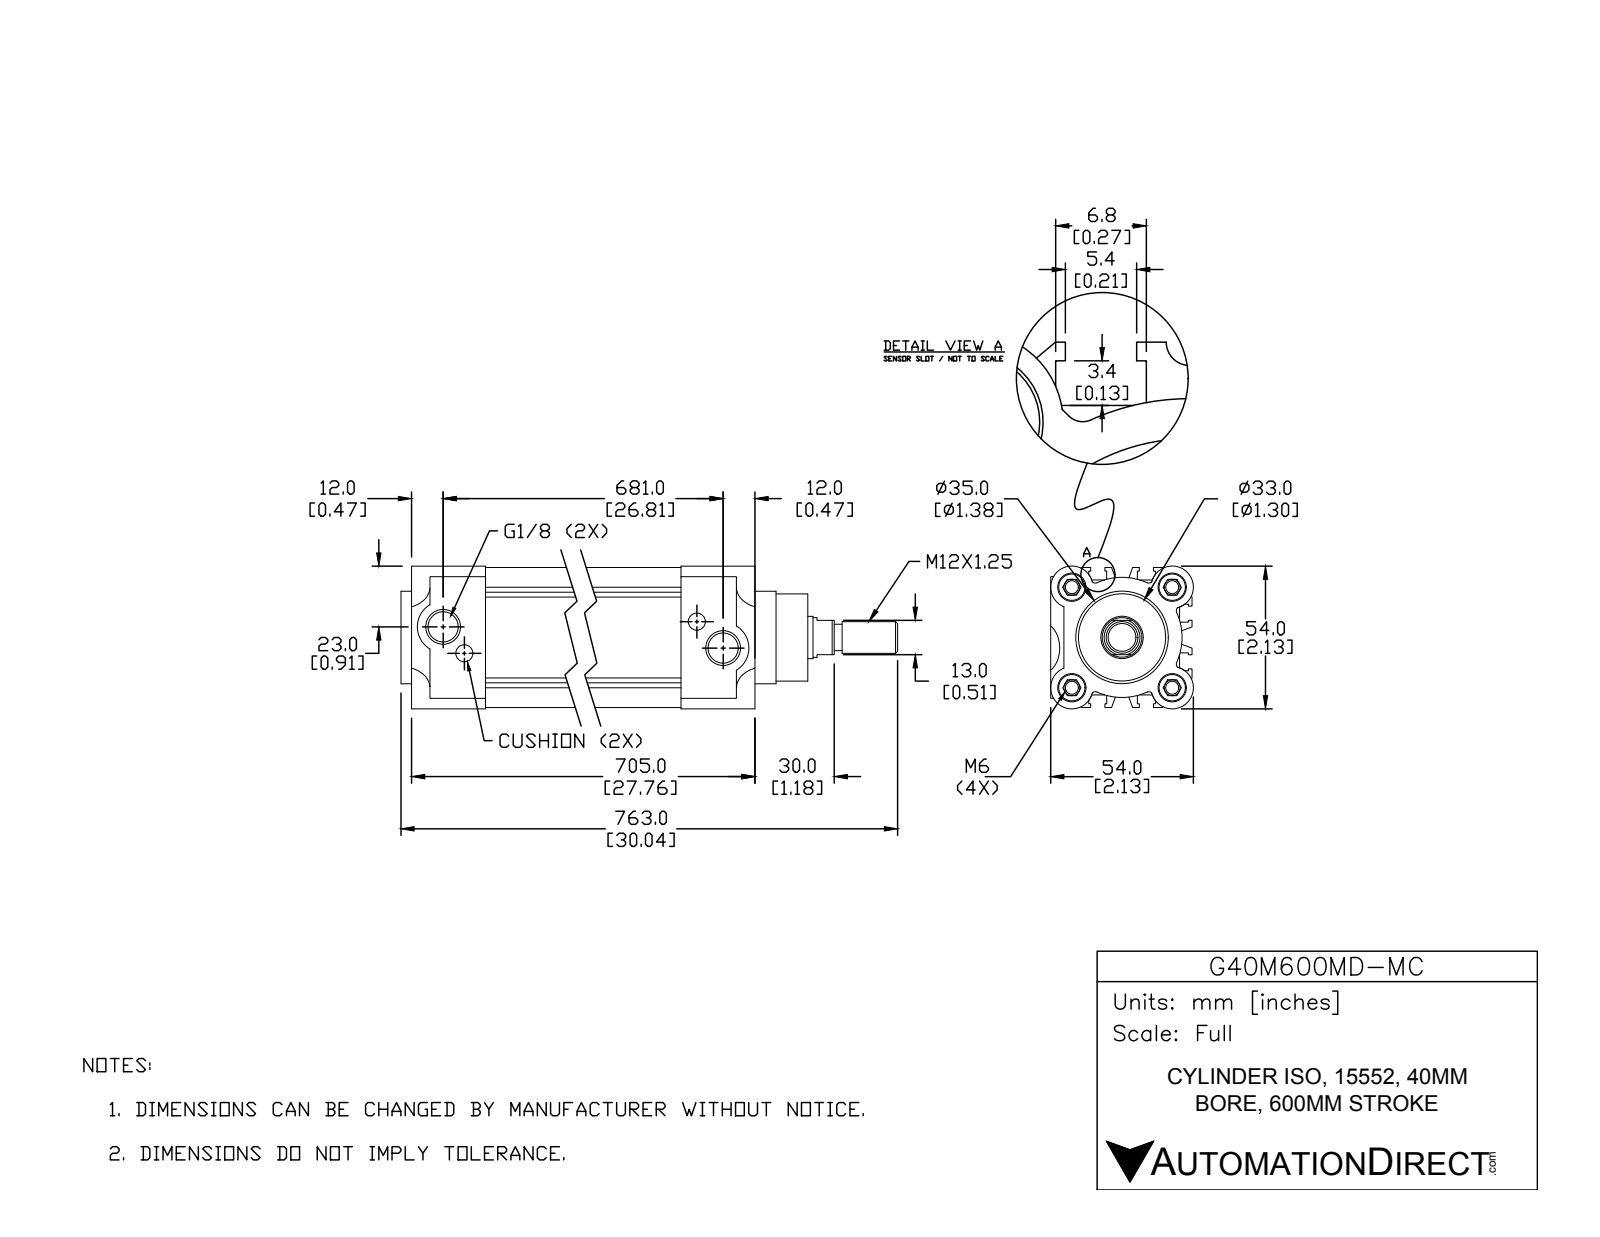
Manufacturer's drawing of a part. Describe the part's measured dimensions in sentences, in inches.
The part is named "40-HL; 40121-HR; G40M600MD-MC; 40121600-R (+1 more)". Its 3-D file was written by "SolidWorks 2015 (CONFIG_CONTROL_DESIGN)". It is 4 solids with 419 faces: 236 planar, 138 cylindrical and 45 other. Overall it measures 30.039 by 2.126 by 2.126 inches. Its volume is 68.71 cubic inches and its surface area 564.1 square inches. Round holes: 4 of diameter 0.194, 4 of diameter 0.421, 2 of diameter 0.256, 2 of diameter 0.451, 1 of diameter 0.63. Round bosses or shafts: 5 of diameter 0.394, 1 of diameter 1.575, 1 of diameter 1.378, 1 of diameter 1.299, 1 of diameter 0.591, 1 of diameter 0.472. Partial cylindrical surfaces (rounded edges, fillets, slot ends): 12 of radius 0.059, 6 of radius 0.004, 4 of radius 0.295, 4 of radius 0.315, 2 of radius 0.384, 1 of radius 0.886, 1 of radius 0.896. The main face-to-face distances are 1.9, 0.187, 2.087, 0.724, 0.954, 1.372, 0.547, 1.539, 0.815, 1.272. The hole center spacings are 1.058, 1.496, 2.116, 0.504, 0.557, 26.107, 26.417, 26.496.
